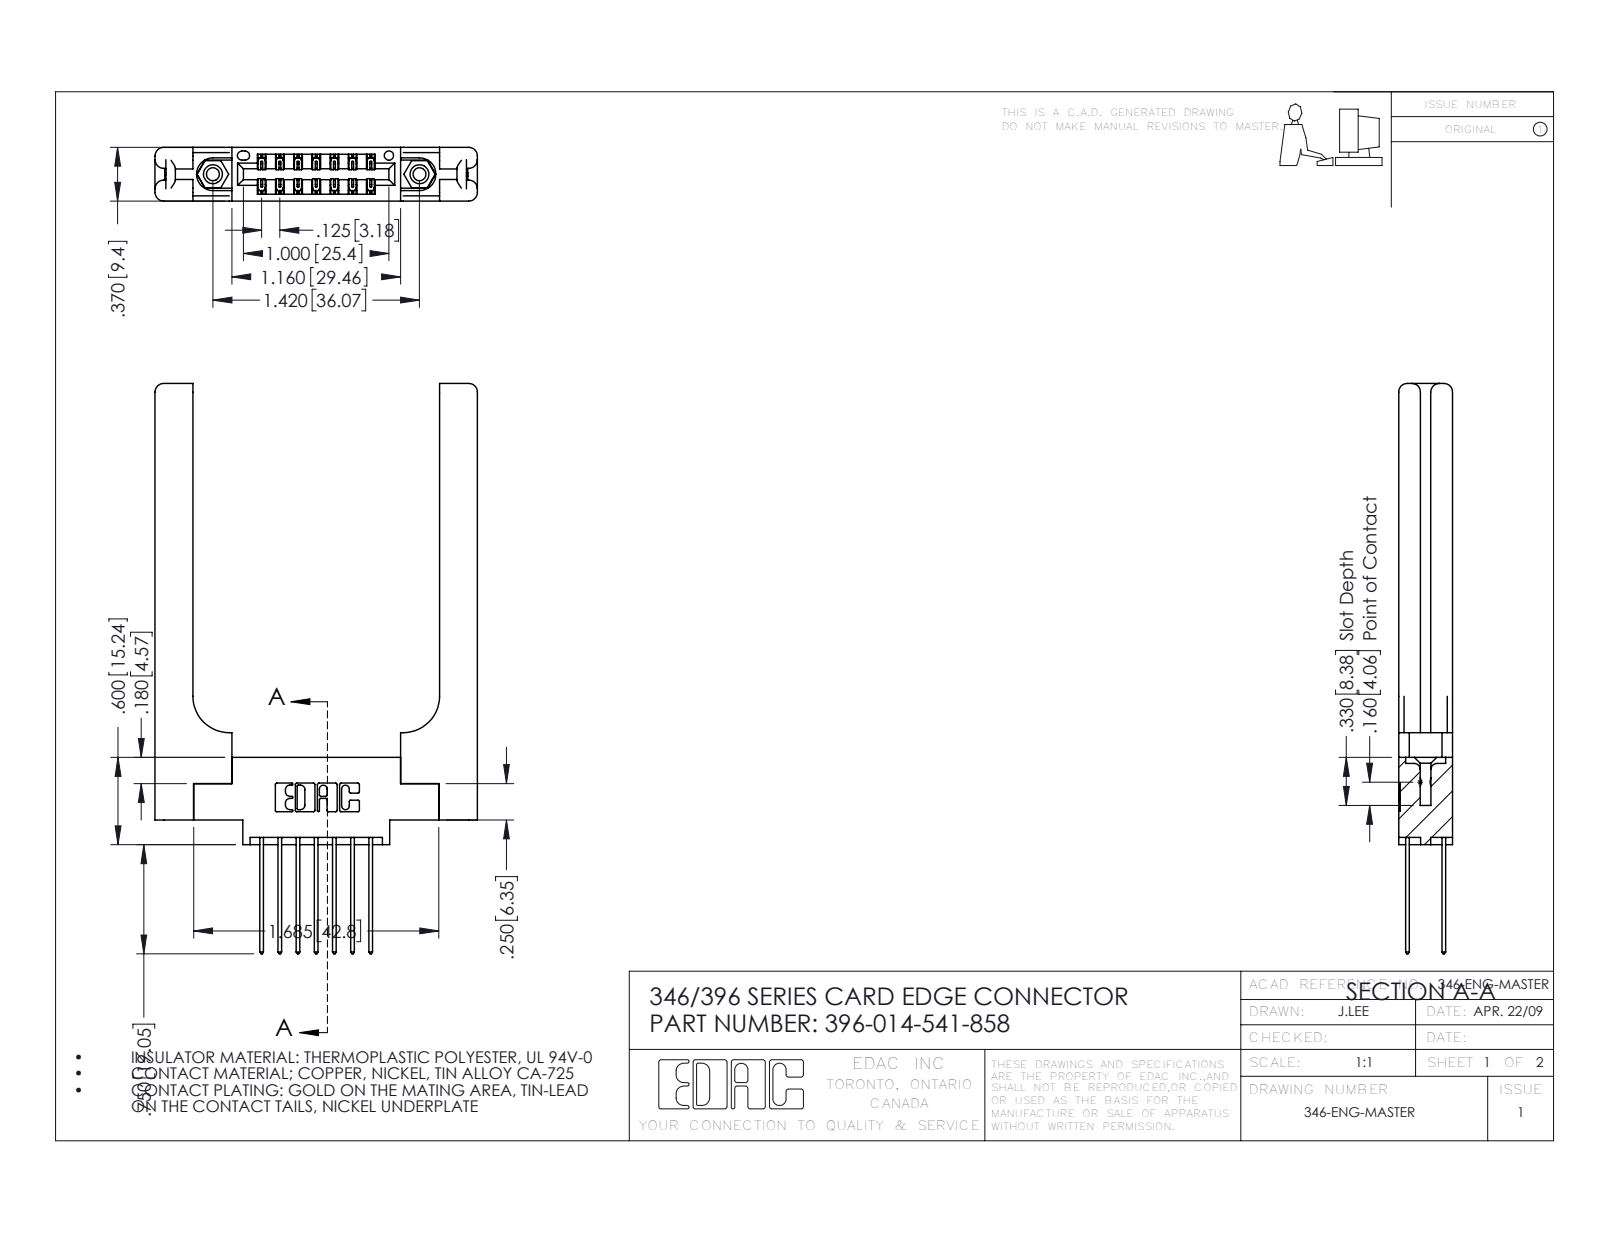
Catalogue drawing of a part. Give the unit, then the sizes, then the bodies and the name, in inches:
Units: inches
Overall size (bounding box): 3.92 × 2.216 × 0.37
Round holes (diameter × count): ⌀0.089 ×2, ⌀0.125 ×2, ⌀0.156 ×2, ⌀0.064 ×1
Round bosses / shafts (diameter × count): ⌀0.155 ×2
Partial cylindrical surfaces — rounded edges, fillets, slot ends (radius × count): R0.01 ×22, R0.006 ×21, R0.06 ×16, R0.01 ×14, R0.007 ×6, R0.031 ×6, R0.026 ×3, R0.014 ×2
Main face-to-face distances: 0.37, 0.15, 0.072, 0.22, 0.148, 0.25, 0.102, 0.048, 0.322, 0.173
Hole centre spacings: 0.246, 1.217, 1.42
Volume: 0.771 in³ · Surface area: 18.69 in²
Bodies: 19 solids, 1110 faces (718 planar, 332 cylindrical, 60 other)
Part name (STEP PRODUCT): 345-292-001_345-293-141; 346 Part_0.170 Offset - 0.156 Dia-TH; 396-014-541-858; 346-220-058_345-220-058 (+1 more)
STEP written by: SolidWorks 2016 (CONFIG_CONTROL_DESIGN)
